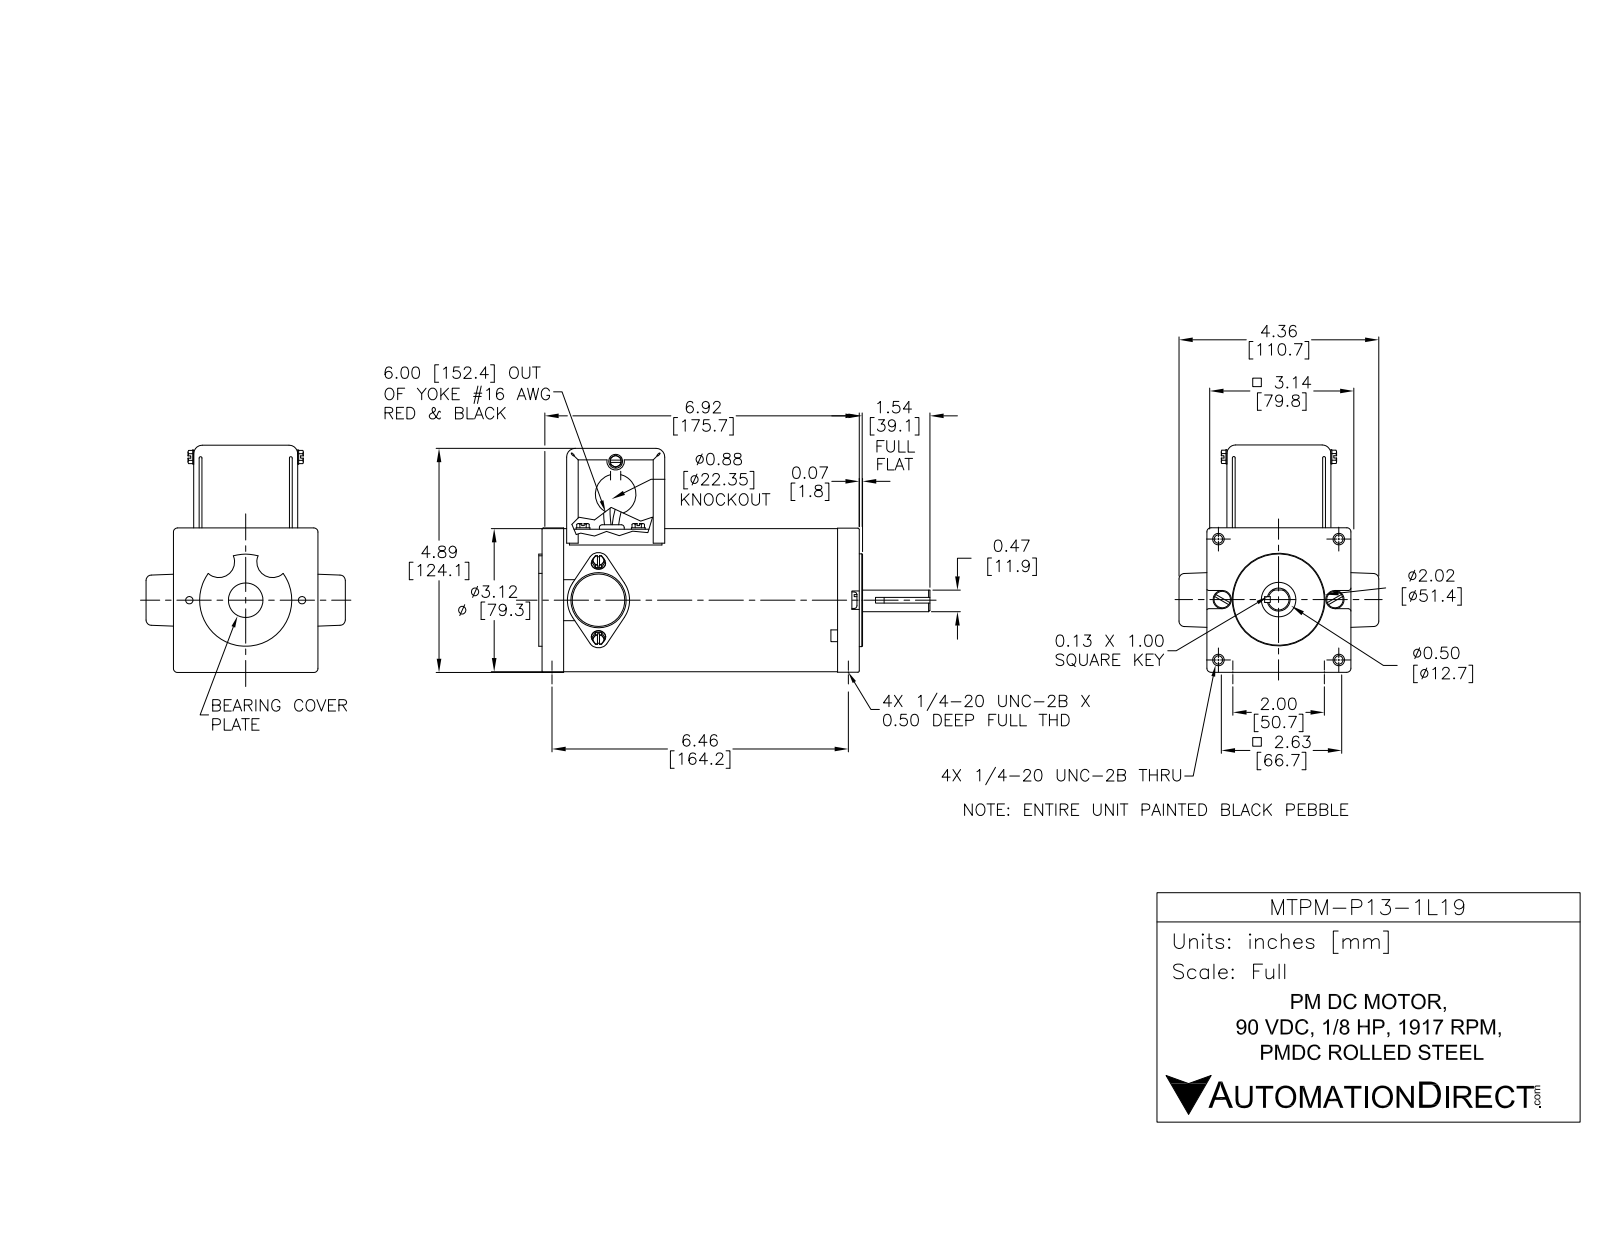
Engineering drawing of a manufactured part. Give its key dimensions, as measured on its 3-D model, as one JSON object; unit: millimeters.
{"part_name": "MTPM-P13-1L19", "step_written_by": "SolidWorks 2015 (AUTOMOTIVE_DESIGN)", "units": "millimeters", "bodies": {"solids": 28, "faces": 401, "planar": 271, "cylindrical": 105, "other": 25}, "overall_size": [216.4, 125.6, 111.5], "volume_mm3": 224200, "surface_area_mm2": 176100, "round_holes": [[3.2, 4], [5, 2], [6.4, 1], [7.6, 1], [9.5, 1], [12.7, 1], [31.1, 1], [76.2, 1], [79.4, 1]], "round_bosses_or_shafts": [[7.6, 4], [3.2, 2], [2.5, 2], [50.8, 1], [15.9, 1], [7.6, 1]], "partial_cylinders_radius": [[4.9, 4], [5.9, 4], [4, 2], [8.7, 2], [15.6, 1], [16.9, 1], [17.2, 1], [40.3, 1]], "face_to_face_distances": [0.8, 6.4, 169.3, 1.6, 54.2, 162.9, 52, 2.4, 175.6, 55.8], "hole_center_spacings": [33.5, 47.2, 66.8, 72.8, 31.2, 94.5, 62.5, 78.3]}
